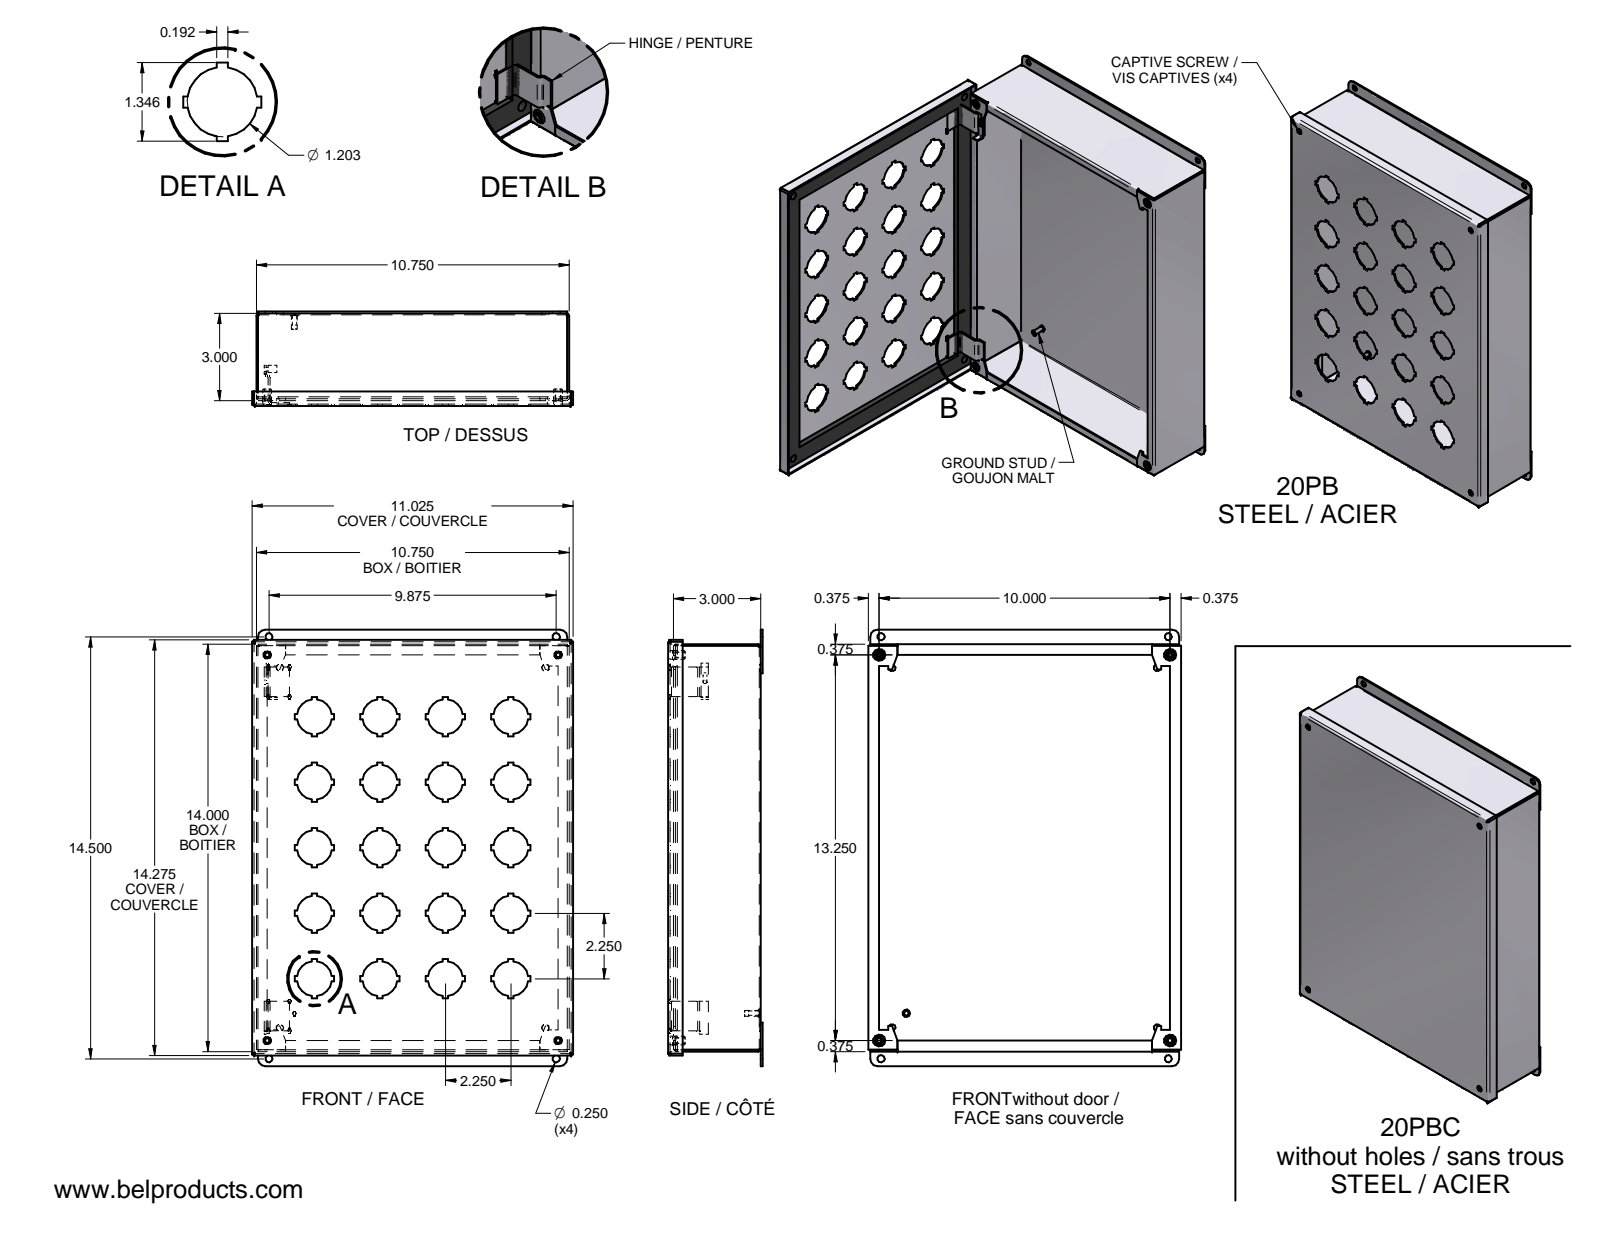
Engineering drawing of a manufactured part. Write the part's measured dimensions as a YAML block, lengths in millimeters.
part_name: "20PBC_COUVERCLE; 20PBC-C; 20PBC_GASKET; PB-PENTURE-1 (+7 more)"
step_written_by: "Unknown (AUTOMOTIVE_DESIGN)"
units: millimeters
bodies: {solids: 13, faces: 1286, planar: 899, cylindrical: 106, other: 281}
overall_size: [381, 280.04, 82.42]
volume: 659074
surface_area: 747932
round_holes:
  - {diameter: 3.17, count: 9}
  - {diameter: 6.35, count: 8}
  - {diameter: 4.04, count: 4}
  - {diameter: 5.49, count: 4}
  - {diameter: 6.22, count: 4}
  - {diameter: 6.73, count: 4}
  - {diameter: 7.37, count: 4}
  - {diameter: 7.92, count: 4}
  - {diameter: 3.45, count: 1}
round_bosses_or_shafts:
  - {diameter: 3.02, count: 9}
  - {diameter: 7.52, count: 4}
  - {diameter: 6.35, count: 4}
  - {diameter: 6.5, count: 1}
  - {diameter: 4.83, count: 1}
  - {diameter: 0.51, count: 1}
partial_cylinders:
  - {radius: 0.81, count: 16}
  - {radius: 2.34, count: 16}
  - {radius: 6.35, count: 4}
  - {radius: 1.59, count: 2}
face_to_face_distances: [1.52, 79.38, 80.9, 77.86, 1.53, 271.53, 354.08, 3.49, 270, 273.06]
hole_center_spacings: [243.14, 252.91, 433.49, 254, 15.72, 15.95, 18.69, 25.65]
